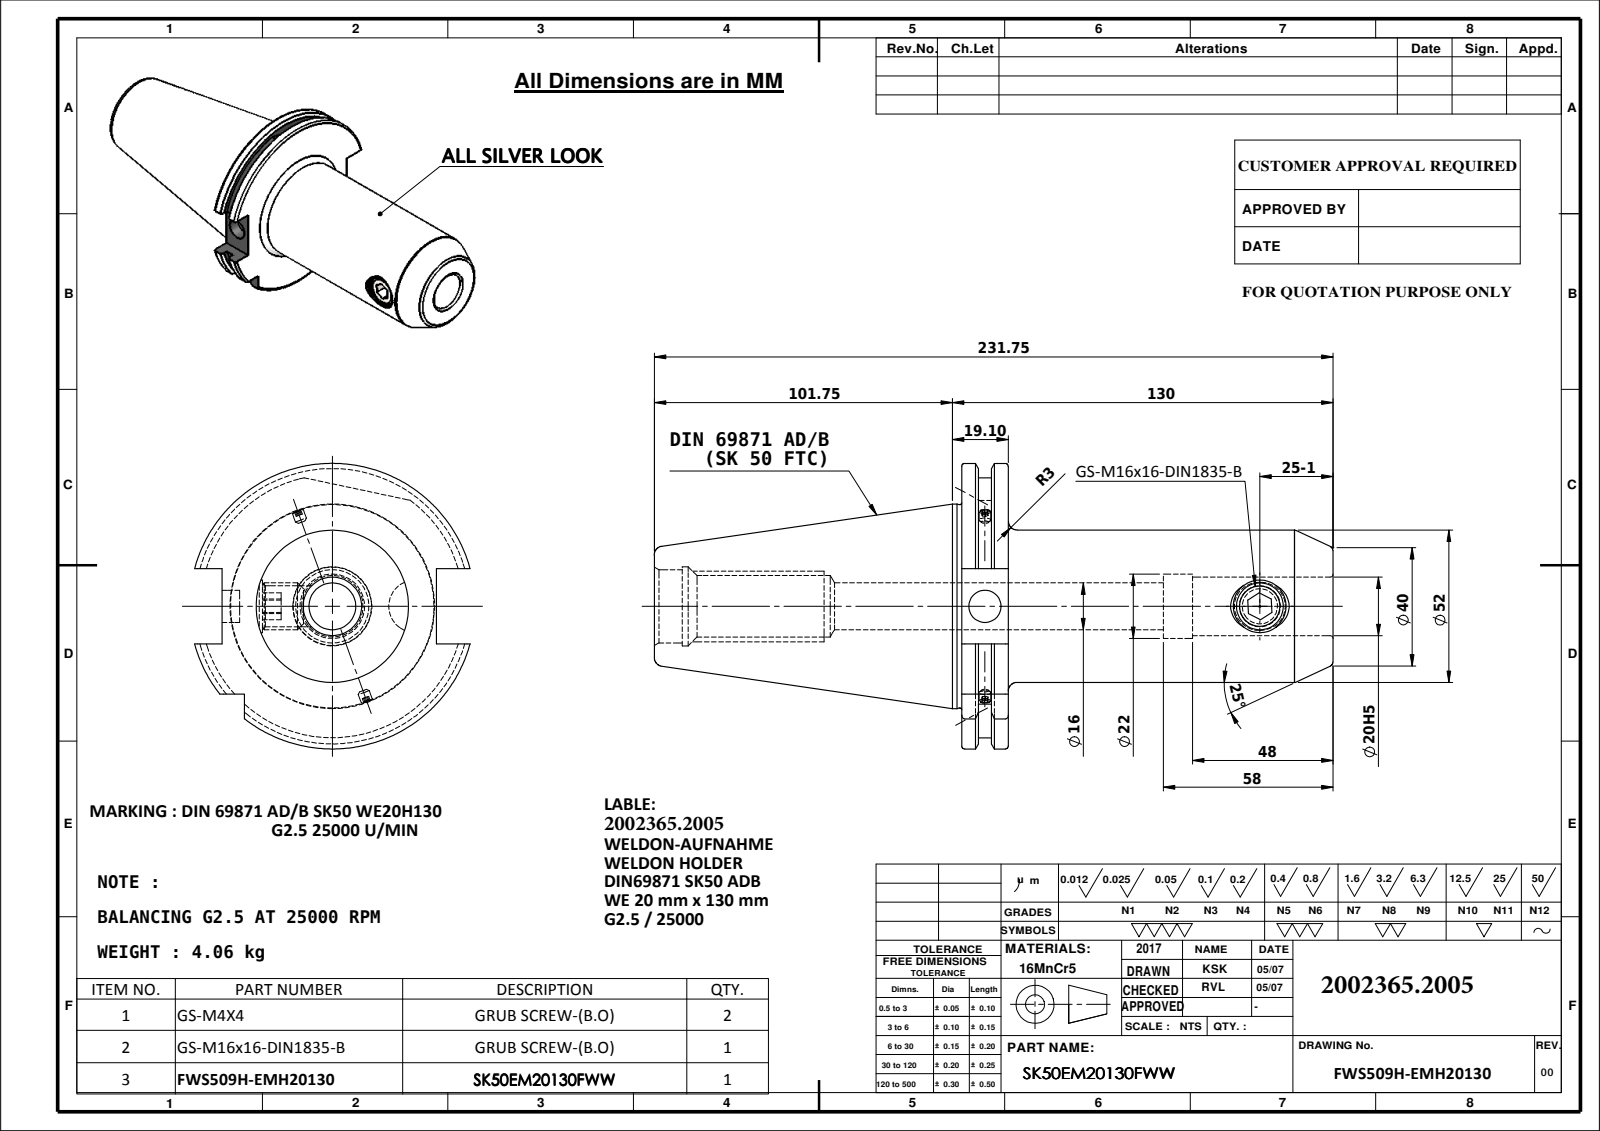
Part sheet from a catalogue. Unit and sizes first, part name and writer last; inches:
Units: inches
Overall size (bounding box): 9.124 × 3.839 × 3.703
Round holes (diameter × count): ⌀0.433 ×1, ⌀0.551 ×1, ⌀0.63 ×1, ⌀0.709 ×1, ⌀0.787 ×1, ⌀0.827 ×1, ⌀0.866 ×1, ⌀0.984 ×1, ⌀1.063 ×1
Round bosses / shafts (diameter × count): ⌀0.157 ×2, ⌀2.75 ×1, ⌀2.734 ×1, ⌀2.047 ×1, ⌀0.63 ×1
Partial cylindrical surfaces — rounded edges, fillets, slot ends (radius × count): R1.768 ×1, R1.919 ×1
Main face-to-face distances: 0.626, 4.992, 4.366, 0.223, 0.403, 4.769, 0.4, 0.177, 0.226, 4.593
Hole centre spacings: 3.697
Volume: 32.15 in³ · Surface area: 106.2 in²
Bodies: 4 solids, 154 faces (51 planar, 43 cylindrical, 60 other)
Part name (STEP PRODUCT): 91506-WE720130; M16X16_ISO 4026 - M16 x 10-N; Copy of M4X4_DIN 913 - M4 x 4-N; SK50EM20130FWW
STEP written by: SolidWorks 2009 (CONFIG_CONTROL_DESIGN)
